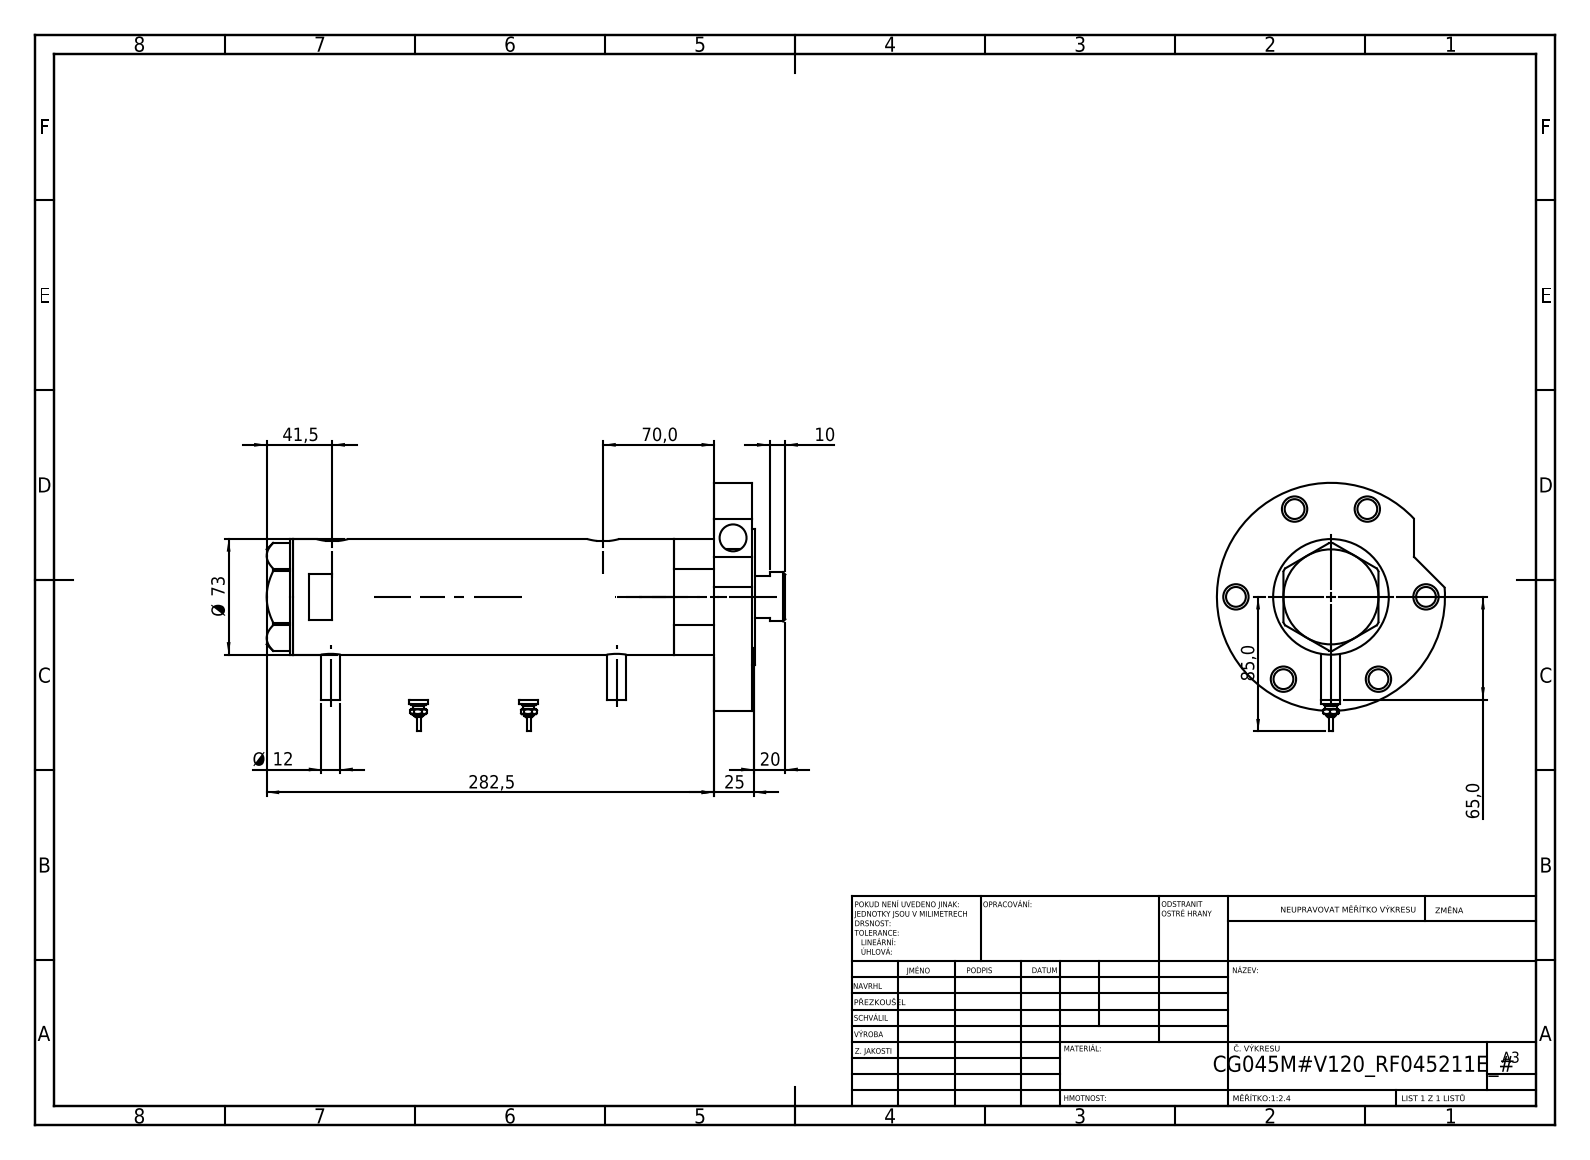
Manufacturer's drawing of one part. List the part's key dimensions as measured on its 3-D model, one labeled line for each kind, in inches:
Part name (STEP PRODUCT): V270CG_BACK; V270CG_RF211E; V270CG_VC; Switch (+2 more)
STEP written by: SolidWorks 2019 (CONFIG_CONTROL_DESIGN)
Units: inches
Bodies: 7 solids, 256 faces (88 planar, 104 cylindrical, 64 other)
Overall size (bounding box): 12.894 × 6.181 × 5.669
Volume: 86.96 in³ · Surface area: 371.7 in²
Round holes (diameter × count): ⌀0.492 ×8, ⌀0.63 ×6, ⌀0.518 ×2, ⌀0.413 ×1, ⌀0.669 ×1, ⌀1.26 ×1, ⌀1.319 ×1, ⌀1.772 ×1, ⌀1.89 ×1, ⌀2.362 ×1, ⌀2.52 ×1
Round bosses / shafts (diameter × count): ⌀0.472 ×4, ⌀0.354 ×2, ⌀0.276 ×2, ⌀0.177 ×2, ⌀0.098 ×2, ⌀5.669 ×1, ⌀3.386 ×1, ⌀2.874 ×1
Partial cylindrical surfaces — rounded edges, fillets, slot ends (radius × count): R0.394 ×2
Main face-to-face distances: 0.945, 10.472, 1.024, 0.079, 11.417, 11.496, 0.039, 7.717, 2.756, 3.701
Hole centre spacings: 2.362, 2.625, 3.928, 4.091, 4.237, 4.714, 0.039, 0.335
